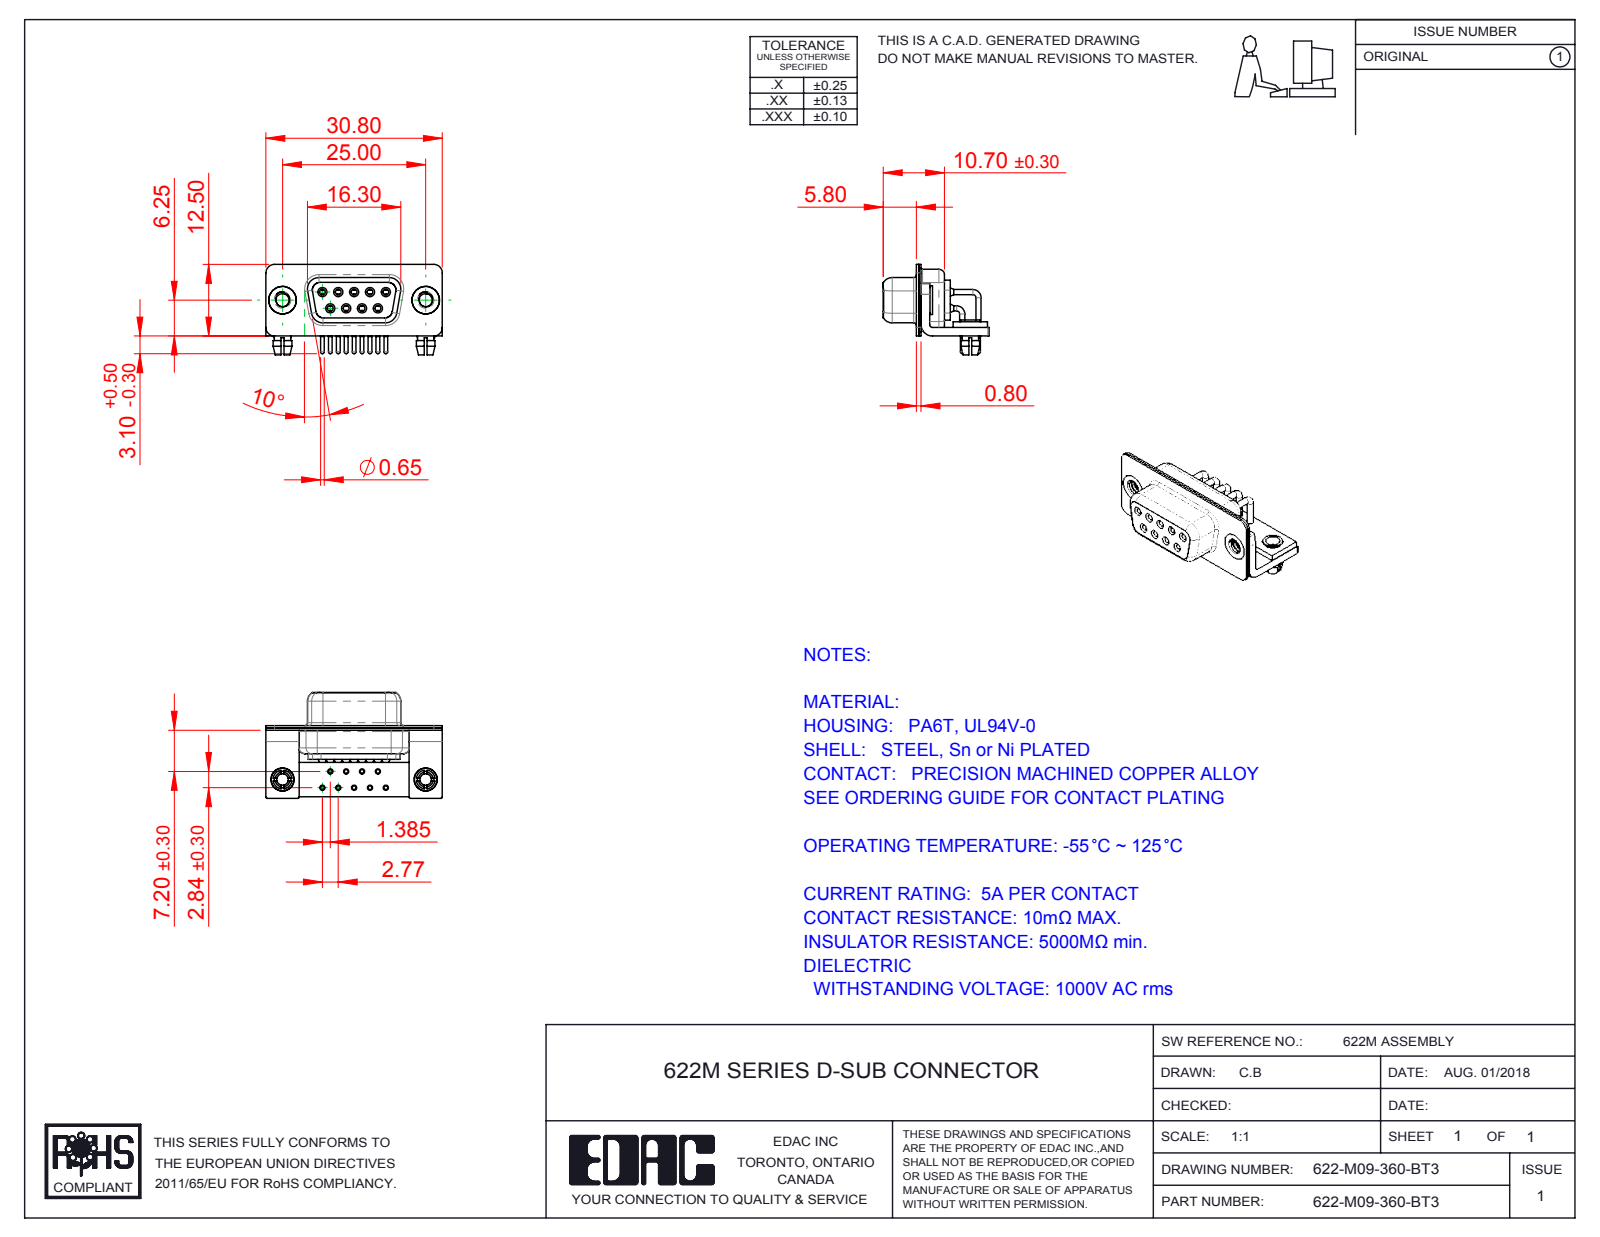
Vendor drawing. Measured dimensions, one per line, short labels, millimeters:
name: 622M 4-40 Threaded Rivet_Stabilizer; 622M Contact Row 2; 622M Contact Row 1; 622-M09-360-BT3 (+6 more)
written by: SolidWorks 2016 (CONFIG_CONTROL_DESIGN)
unit: mm
bodies: 19 solids, 916 faces (276 planar, 416 cylindrical, 224 other)
size: 30.8 × 18.5 × 15.8
volume: 2 177 mm³; area: 5 763 mm²
holes: 11× ⌀2, 9× ⌀0.9, 9× ⌀1, 9× ⌀1.1, 9× ⌀1.7, 9× ⌀1.8, 2× ⌀2.26, 2× ⌀2.5, 2× ⌀3.2, 2× ⌀4, 2× ⌀4.8
bosses: 9× ⌀1.6, 9× ⌀1.5, 9× ⌀0.9, 9× ⌀0.65, 2× ⌀5, 2× ⌀4.9, 2× ⌀4, 2× ⌀3.4
rounds: 16× R0.25, 16× R1.5, 13× R2, 8× R1.35, 8× R1.6, 5× R0.5, 4× R0.6, 4× R0.65
face distances: 0.4, 0.8, 1.5, 2.3, 1.9, 1, 9.35, 1.45, 8.95, 0.85
hole spacings: 3.16, 2.77, 5.54, 5.03, 5.04, 8.31, 7.48, 7.49
